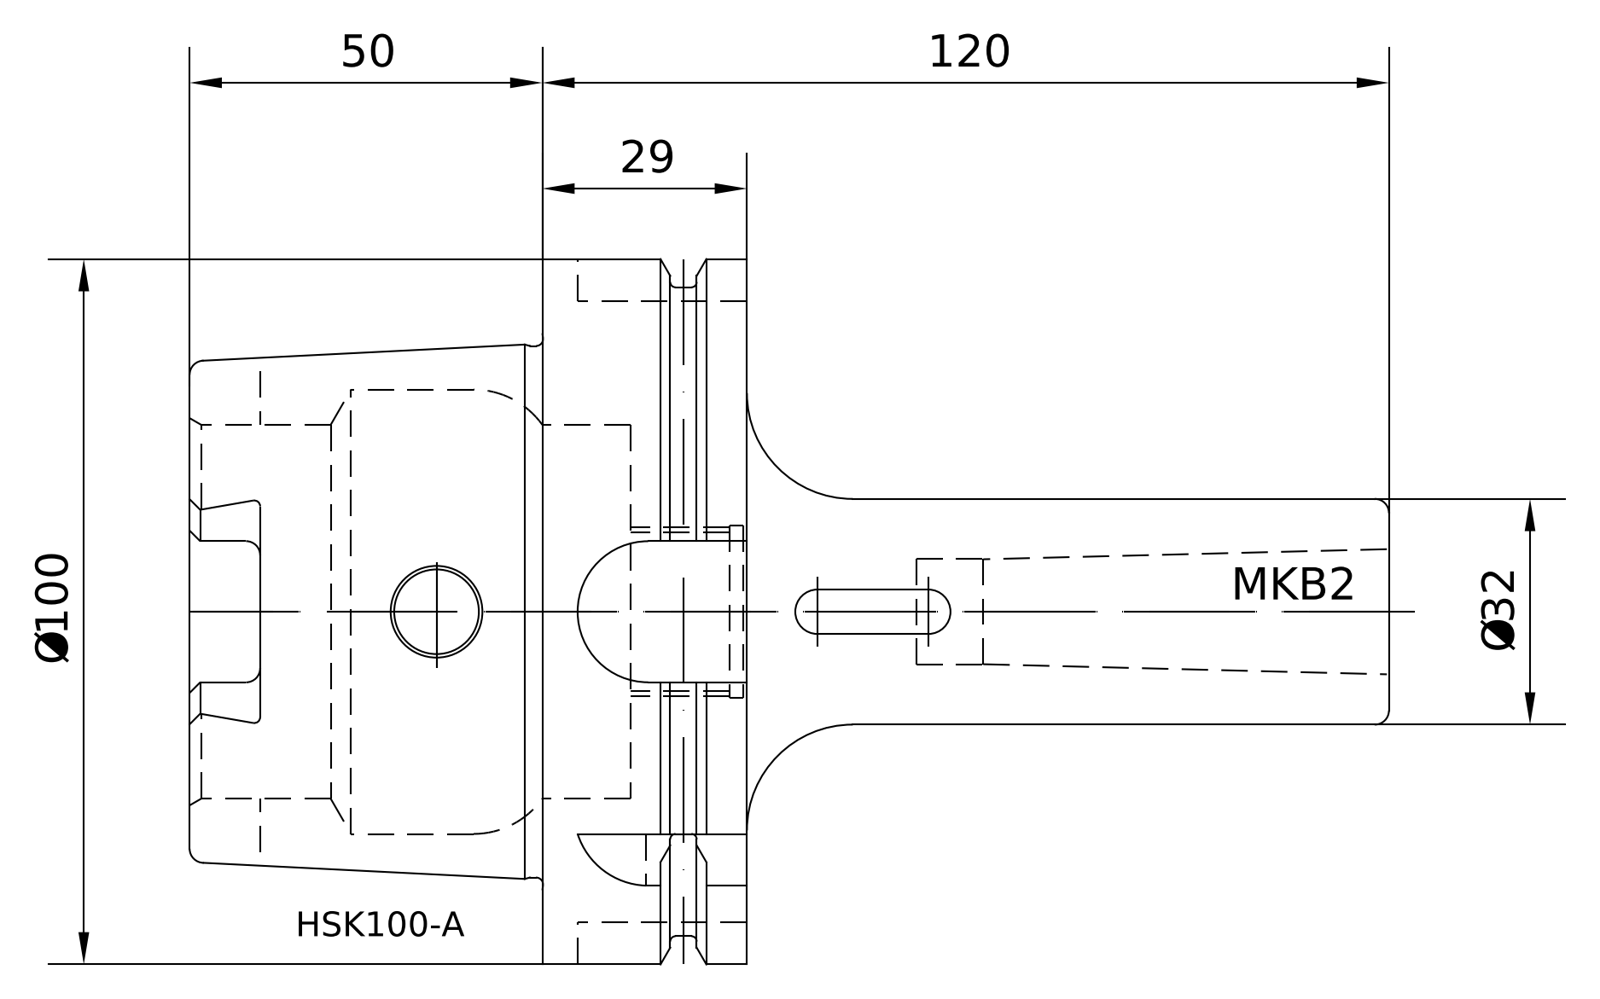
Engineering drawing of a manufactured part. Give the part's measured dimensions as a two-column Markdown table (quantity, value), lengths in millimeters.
| quantity | value |
| --- | --- |
| part name | A100-080-02 |
| STEP written by | PRO/ENGINEER BY PARAMETRIC TECHNOLOGY CORPORATION, 2010430 (CONFIG_CONTROL_DESIGN) |
| units | millimeters |
| bodies | 1 solid, 174 faces (50 planar, 51 cylindrical, 73 other) |
| overall size | 170 × 100 × 100 |
| volume | 319 432 mm³ |
| surface area | 62 074 mm² |
| round holes (diameter × count) | 10 × 1, 12 × 1, 14.9 × 1, 22.5 × 1, 24 × 1, 24.32 × 1, 24.5 × 1, 53 × 1, 63 × 1 |
| round bosses / shafts (diameter × count) | 100 × 1, 92 × 1, 75.36 × 1, 32 × 1 |
| partial cylindrical surfaces (radius × count) | 2 × 6, 5 × 4, 8 × 1, 10 × 1, 11 × 1 |
| main face-to-face distances | 29, 12.5, 16.5, 50, 62.5, 79, 88, 78.5, 28.5, 16 |
